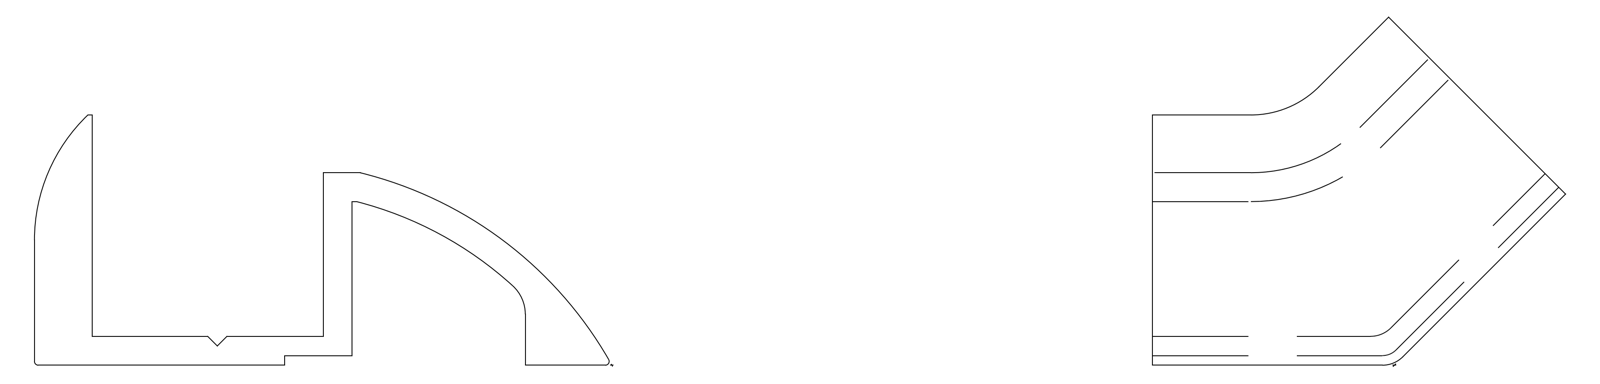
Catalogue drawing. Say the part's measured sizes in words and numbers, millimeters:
Its 3-D file was written by "THINKDESIGN (CONFIG_CONTROL_DESIGN)". It is 0 solids with 37 faces: 26 planar, 9 cylindrical and 2 other. Overall it measures 30.13 by 21.42 by 18.06 millimeters. Partial cylindrical surfaces (rounded edges, fillets, slot ends): 2 of radius 2, 2 of radius 9, 2 of radius 19.09, 2 of radius 20.59, 1 of radius 7. The main face-to-face distances are 1.5, 12, 13.5, 3, 15, 16.5, 0.5, 1, 25.5, 22.5.
